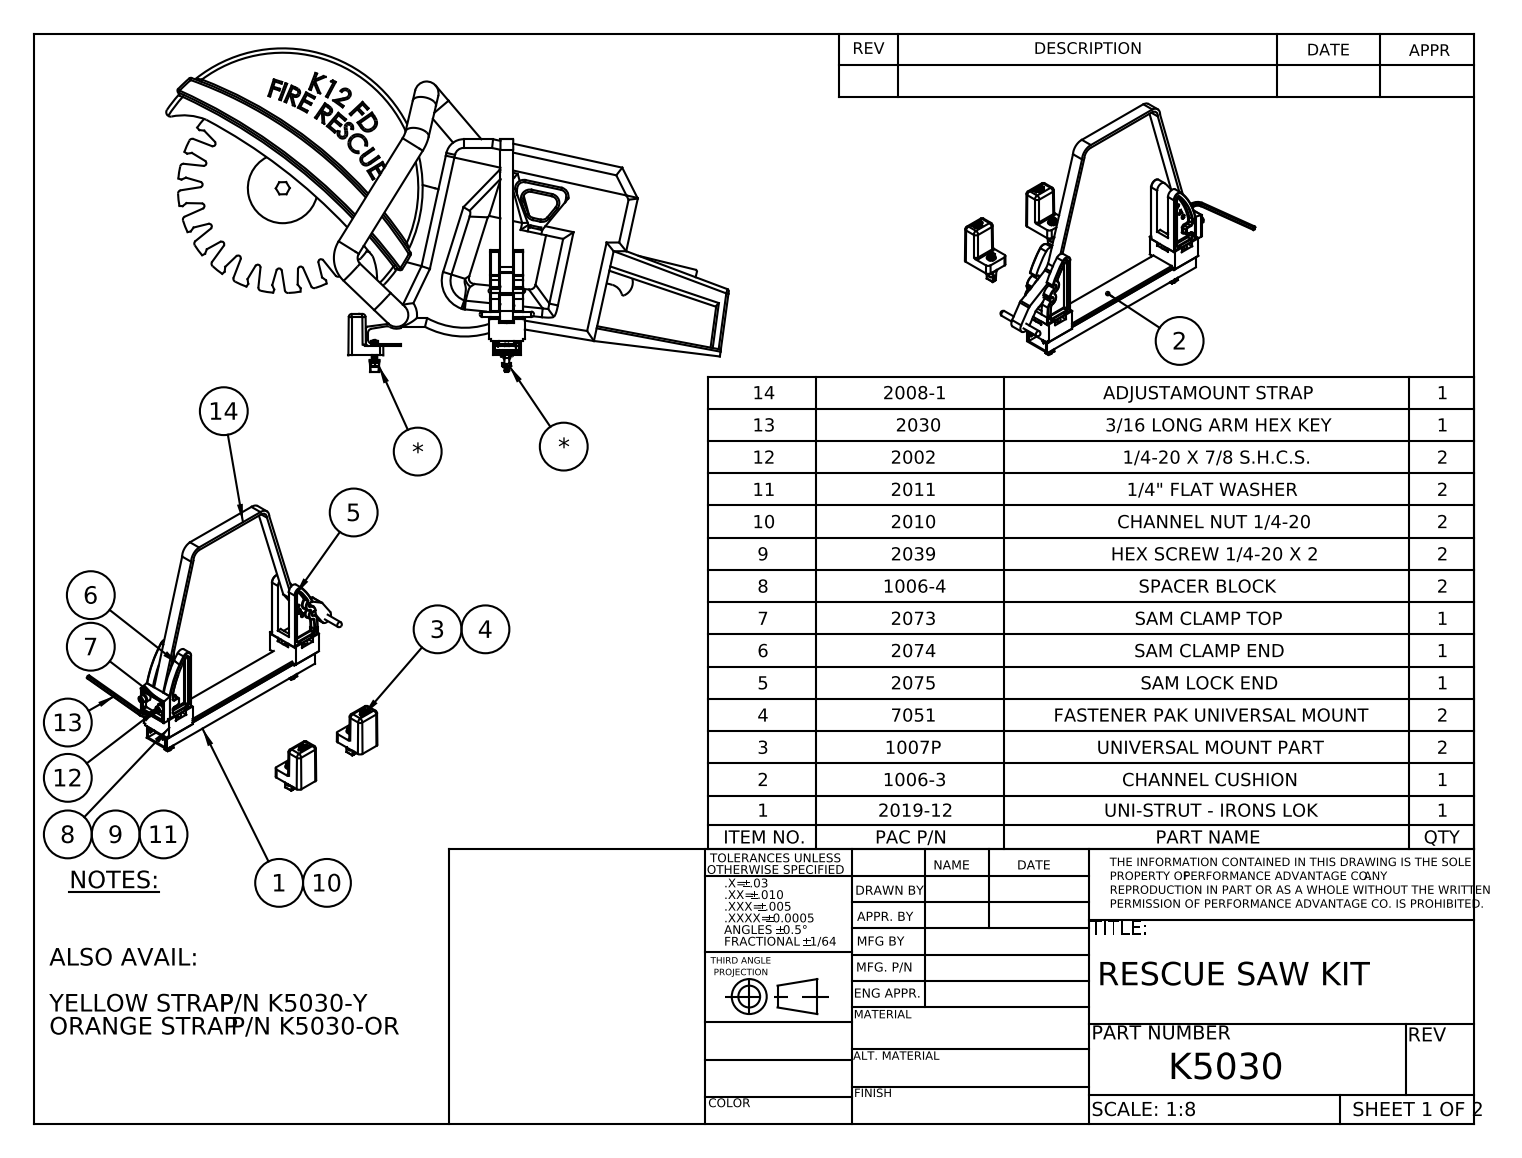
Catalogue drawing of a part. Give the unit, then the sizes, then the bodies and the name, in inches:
Units: inches
Overall size (bounding box): 32.177 × 18.511 × 15.457
Round holes (diameter × count): ⌀0.201 ×8, ⌀0.266 ×8, ⌀0.313 ×8, ⌀0.26 ×4, ⌀0.269 ×4, ⌀0.206 ×2, ⌀0.25 ×2, ⌀0.266 ×2, ⌀0.288 ×2, ⌀0.531 ×2, ⌀0.687 ×2
Round bosses / shafts (diameter × count): ⌀0.25 ×7, ⌀1.357 ×6, ⌀0.404 ×4, ⌀0.375 ×4, ⌀0.187 ×4, ⌀0.625 ×2, ⌀0.452 ×2, ⌀0.437 ×2
Partial cylindrical surfaces — rounded edges, fillets, slot ends (radius × count): R0.031 ×36, R0.125 ×34, R0.188 ×32, R0.5 ×29, R0.156 ×24, R0.25 ×16, R0.015 ×12, R0.062 ×12
Main face-to-face distances: 0.5, 0.25, 1.5, 0.125, 0.125, 1.25, 0.875, 1, 0.625, 0.625
Hole centre spacings: 0.687, 10.223, 10.246, 4.95, 0.576, 0.688, 0.972, 10.911
Volume: 902.6 in³ · Surface area: 2 158 in²
Bodies: 46 solids, 3492 faces (1250 planar, 791 cylindrical, 1451 other)
Part name (STEP PRODUCT): 2039_HBOLT 0.2500-20x1x1-N; 1007P; blade; 2031_CR-FHMS 0.25-20x0.75x0.75-N (+8 more)
STEP written by: SolidWorks 2014 (CONFIG_CONTROL_DESIGN)
